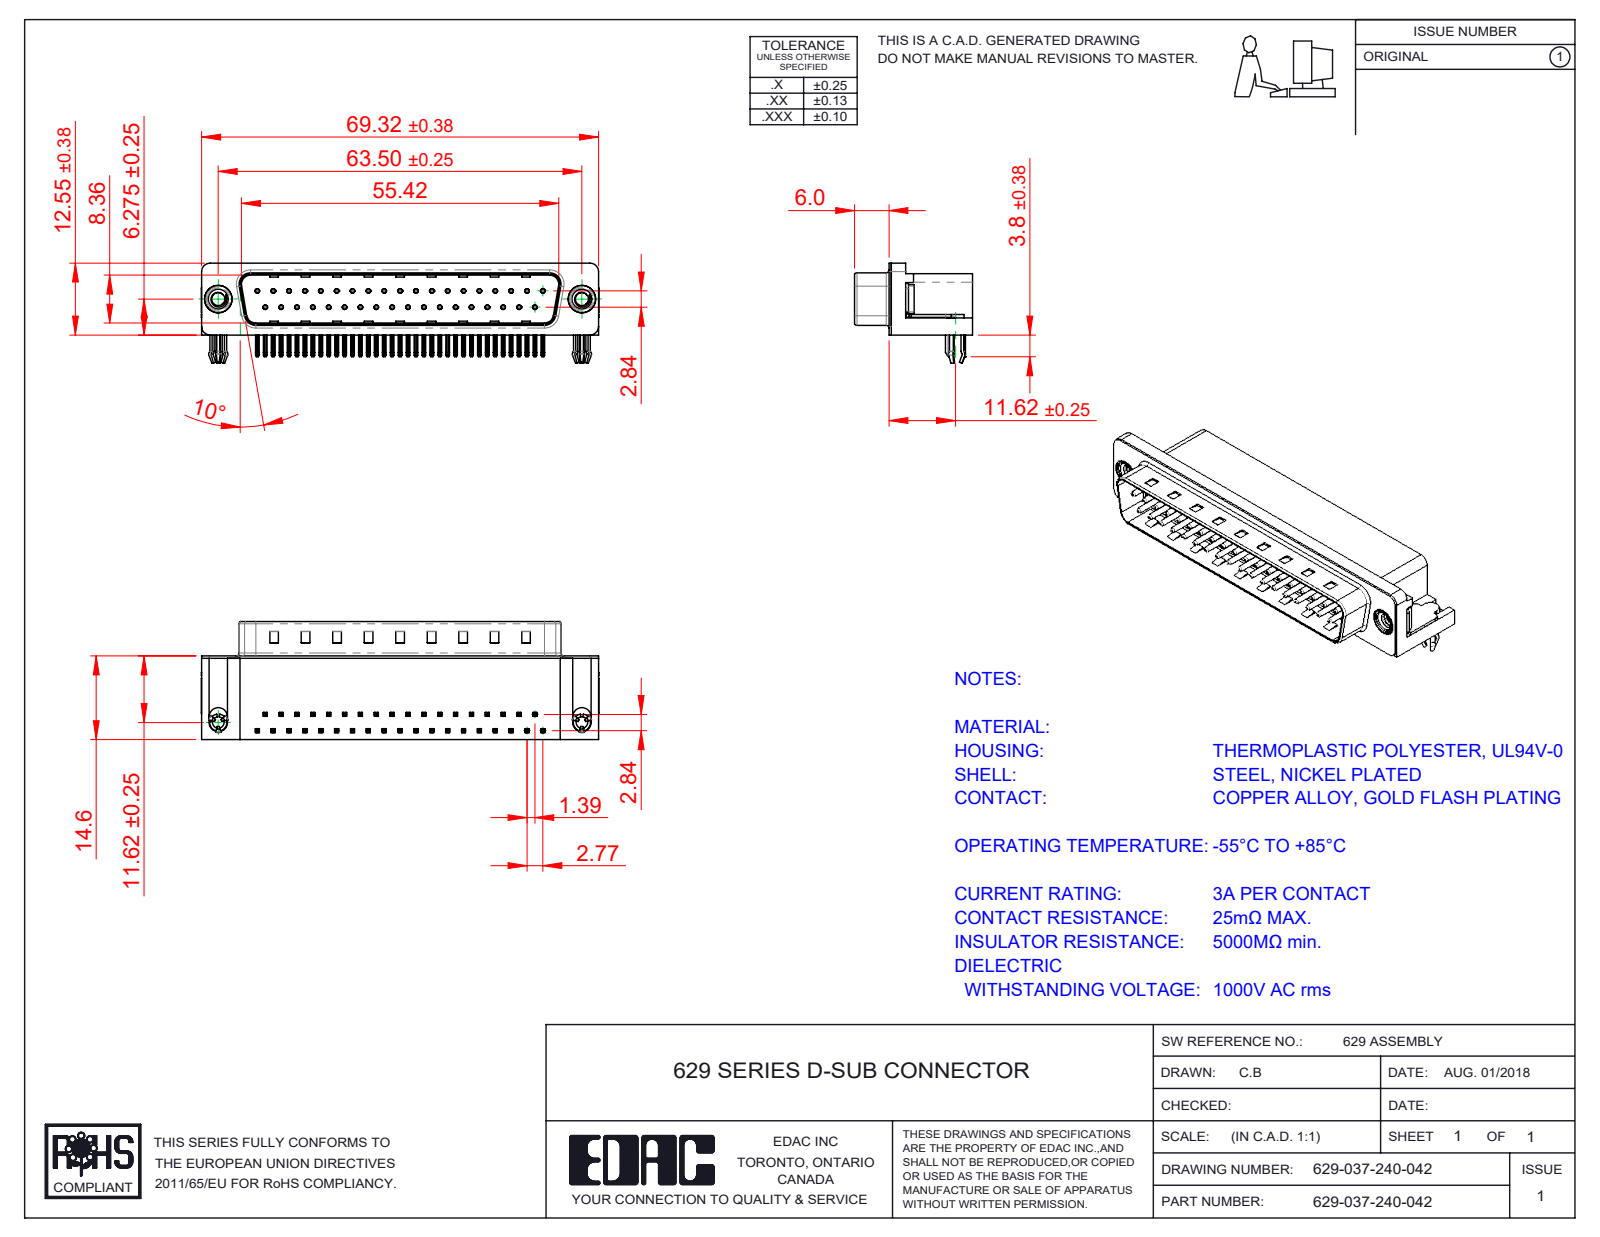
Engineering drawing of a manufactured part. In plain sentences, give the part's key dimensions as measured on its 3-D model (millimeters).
The part is named "629 Shell_37 Socket; 629 Contact Top; 629 3 Prong Board Lock; 629-037-240-042 (+3 more)". Its 3-D file was written by "SolidWorks 2020 (CONFIG_CONTROL_DESIGN)". It is 43 solids with 3301 faces: 2049 planar, 921 cylindrical and 331 other. Overall it measures 69.4 by 20.6 by 17.48 millimeters. Its volume is 9 980 cubic millimeters and its surface area 10 886 square millimeters. Round holes: 37 of diameter 0.35, 37 of diameter 0.8, 2 of diameter 2, 2 of diameter 2.26, 2 of diameter 4, 2 of diameter 4.8, 2 of diameter 5. Round bosses or shafts: 37 of diameter 0.75, 2 of diameter 4.9, 2 of diameter 4.75, 2 of diameter 3.9, 2 of diameter 3. Partial cylindrical surfaces (rounded edges, fillets, slot ends): 160 of radius 0.25, 74 of radius 0.12, 16 of radius 1, 9 of radius 0.5, 8 of radius 1.6, 7 of radius 1.5, 4 of radius 0.9, 4 of radius 2. The main face-to-face distances are 0.4, 10.35, 14.2, 8.76, 2.1, 1.7, 10.46, 10.86, 14.6, 10.11. The hole center spacings are 2.77, 3.16, 5.54, 8.31, 11.08, 13.85, 16.62, 19.39.
